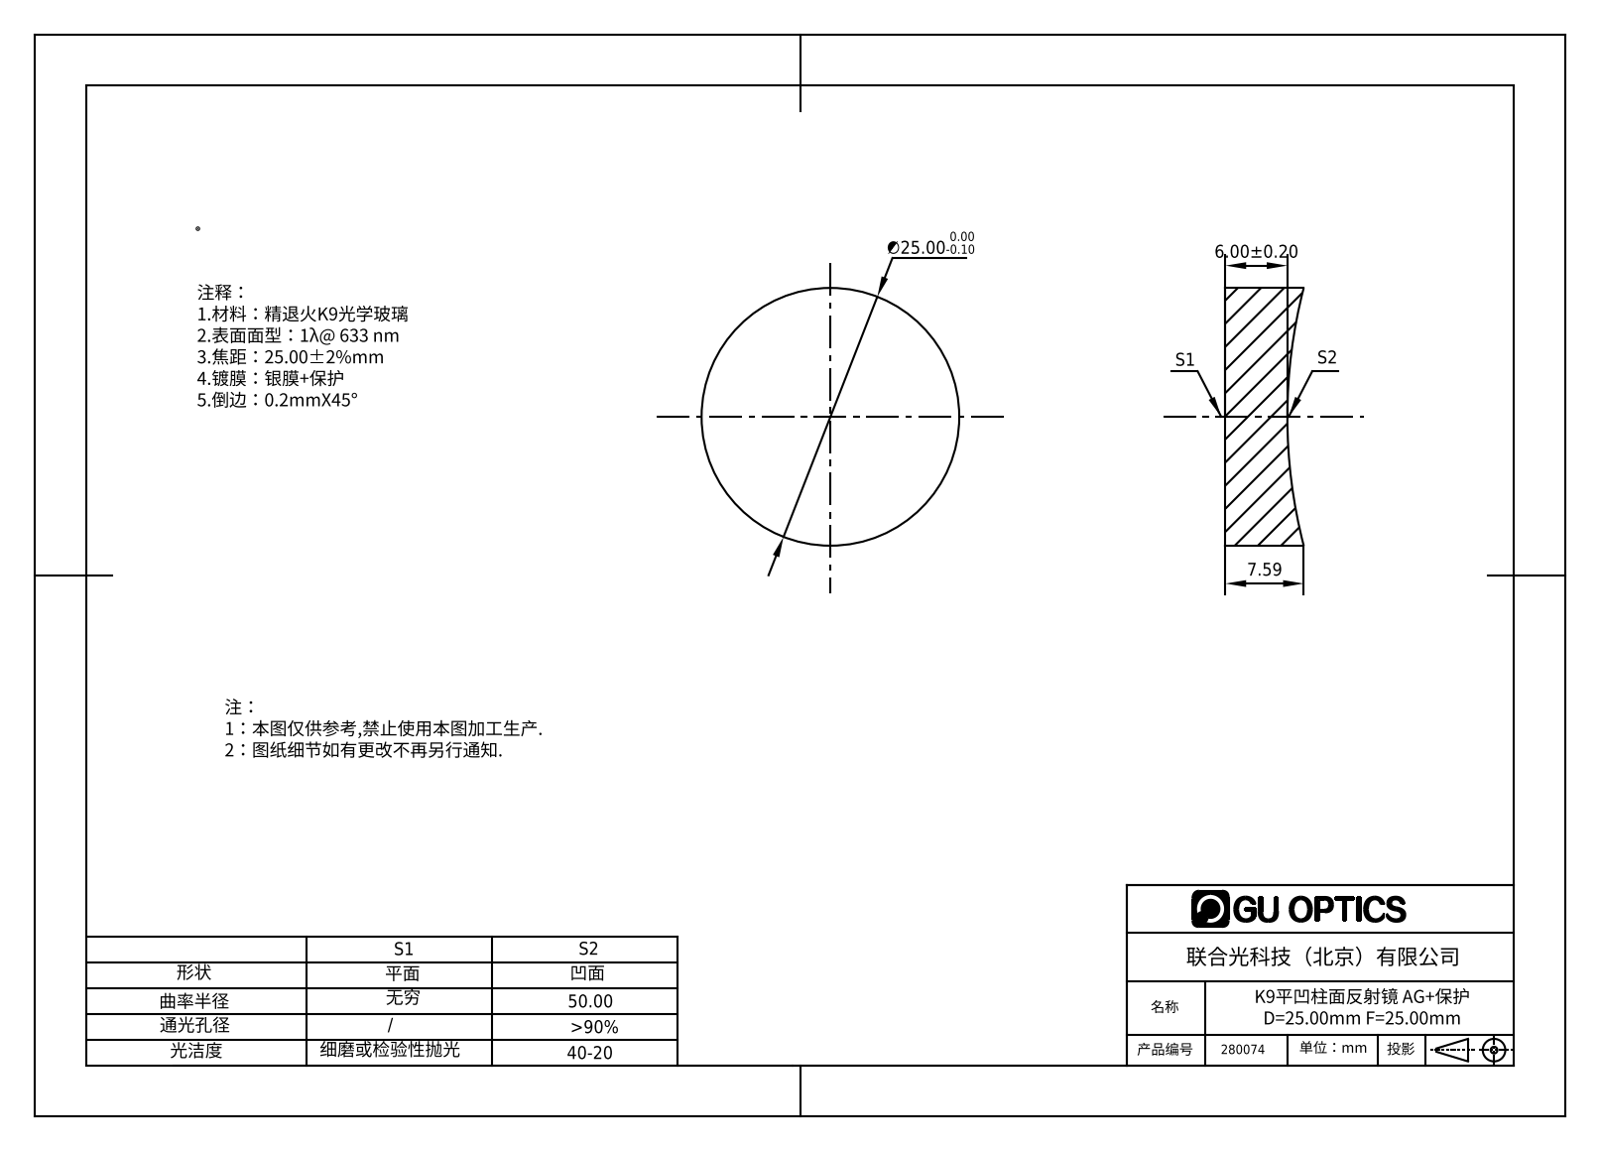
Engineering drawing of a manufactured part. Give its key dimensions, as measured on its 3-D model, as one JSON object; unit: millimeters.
{"part_name": "280008", "step_written_by": "SolidWorks 2020 (CONFIG_CONTROL_DESIGN)", "units": "millimeters", "bodies": {"solids": 1, "faces": 3, "planar": 1, "cylindrical": 2, "other": 0}, "overall_size": [25, 25, 7.59], "volume_mm3": 3139, "surface_area_mm2": 1519, "round_bosses_or_shafts": [[25, 1]], "partial_cylinders_radius": [[50, 1]]}
